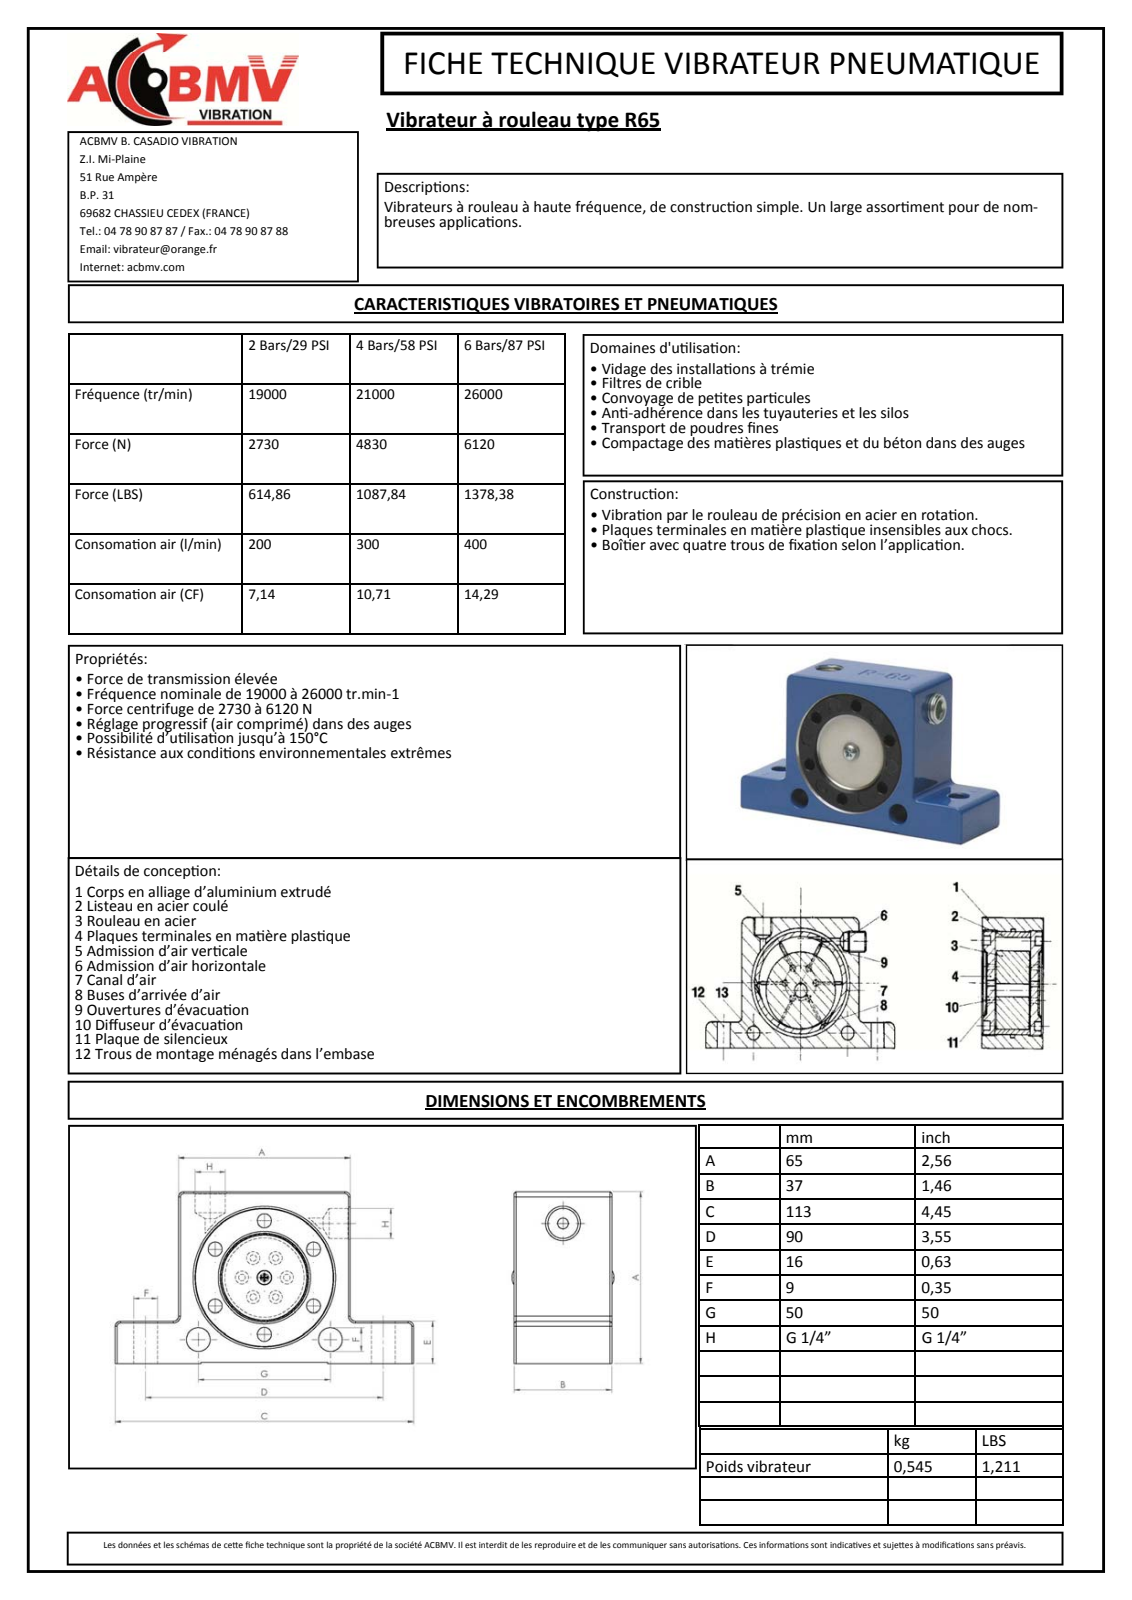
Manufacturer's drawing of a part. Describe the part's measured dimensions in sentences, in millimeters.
The part is named "3065-00-M". Its 3-D file was written by "Autodesk Inventor 2011 (CONFIG_CONTROL_DESIGN)". It is 1 solid with 385 faces: 192 planar, 97 cylindrical and 96 other. Overall it measures 113 by 65 by 38.64 millimeters. Its volume is 167 073 cubic millimeters and its surface area 31 250 square millimeters. Round holes: 7 of diameter 2.5, 6 of diameter 5.3, 4 of diameter 9, 2 of diameter 4, 2 of diameter 11.45, 1 of diameter 2.09, 1 of diameter 3.4. Round bosses or shafts: 1 of diameter 2.9, 1 of diameter 1.88. Partial cylindrical surfaces (rounded edges, fillets, slot ends): 10 of radius 0.25, 6 of radius 2, 5 of radius 1.65, 5 of radius 2.15, 4 of radius 0.54, 3 of radius 0.36, 3 of radius 0.63, 3 of radius 0.72. The main face-to-face distances are 0.5, 65, 37, 36.5, 64.5, 1.76, 35.24, 1.26, 34.74, 1.56. The hole center spacings are 8.5, 14.76, 21.5, 23.12, 29.17, 14.72, 37.24, 17.
